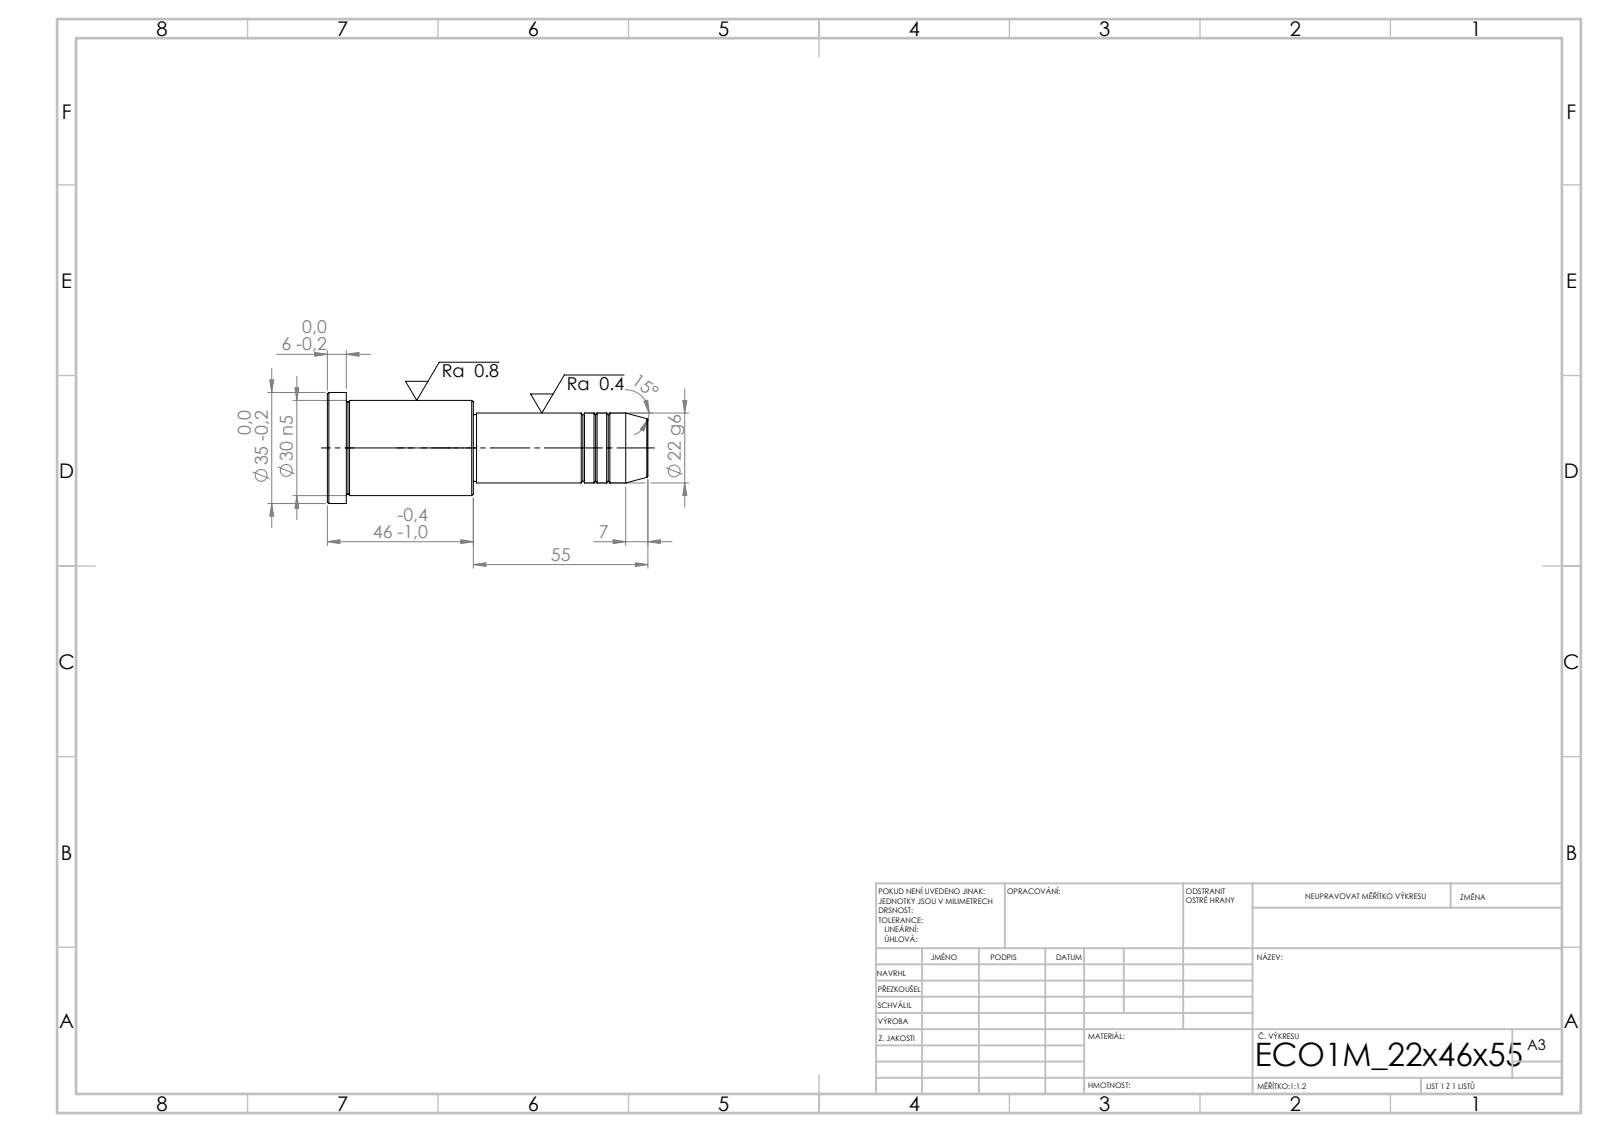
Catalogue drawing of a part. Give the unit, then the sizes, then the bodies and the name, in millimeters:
Units: millimetres
Overall size (bounding box): 101 × 35 × 35
Round bosses / shafts (diameter × count): ⌀35 ×1, ⌀30 ×1, ⌀22 ×1, ⌀21 ×1
Main face-to-face distances: 46, 40, 6, 55, 95, 101, 54, 1, 41, 47
Volume: 54 349 mm³ · Surface area: 10 168 mm²
Bodies: 1 solid, 43 faces (5 planar, 14 cylindrical, 24 other)
STEP written by: SolidWorks 2019 (CONFIG_CONTROL_DESIGN)
